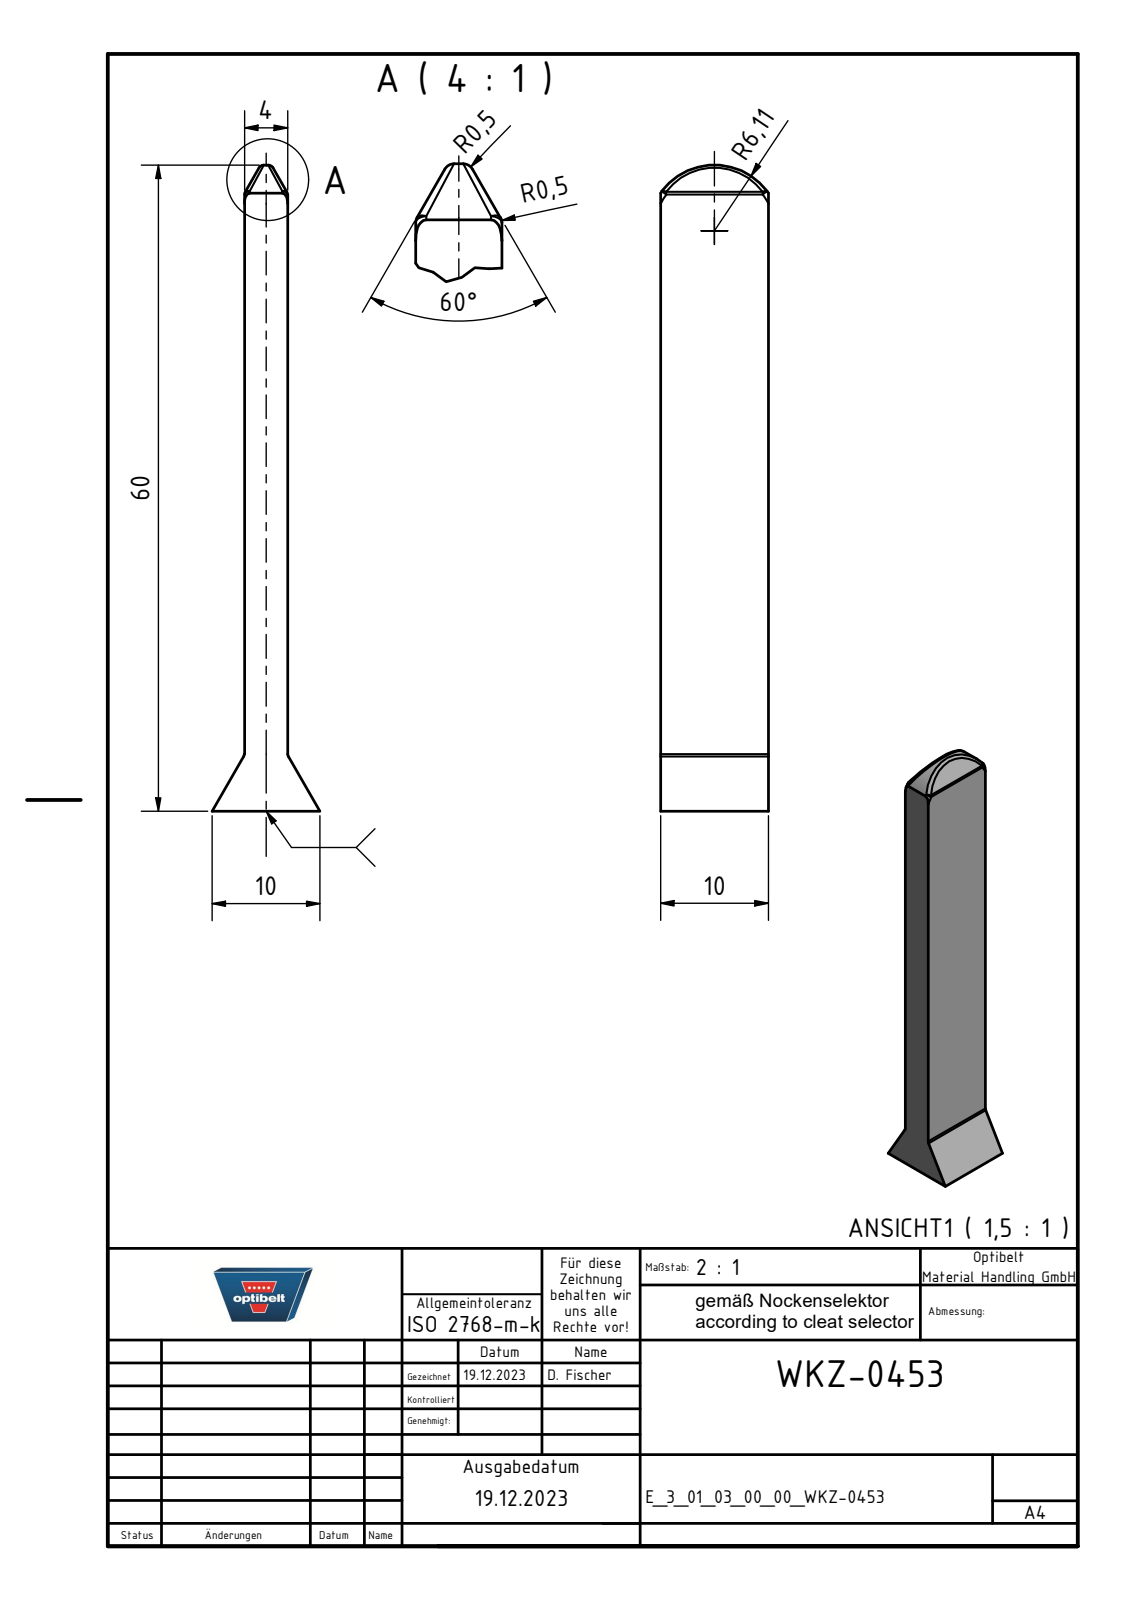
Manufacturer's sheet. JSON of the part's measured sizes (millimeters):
{"part_name": "E_3_01_03_00_00_WKZ-0453", "step_written_by": "Autodesk Inventor 2021 (AUTOMOTIVE_DESIGN)", "units": "millimeters", "bodies": {"solids": 1, "faces": 24, "planar": 9, "cylindrical": 5, "other": 10}, "overall_size": [60, 10, 10], "volume_mm3": 2502, "surface_area_mm2": 1818, "partial_cylinders_radius": [[0.5, 4], [6.11, 1]], "face_to_face_distances": [4, 10, 26.1]}
